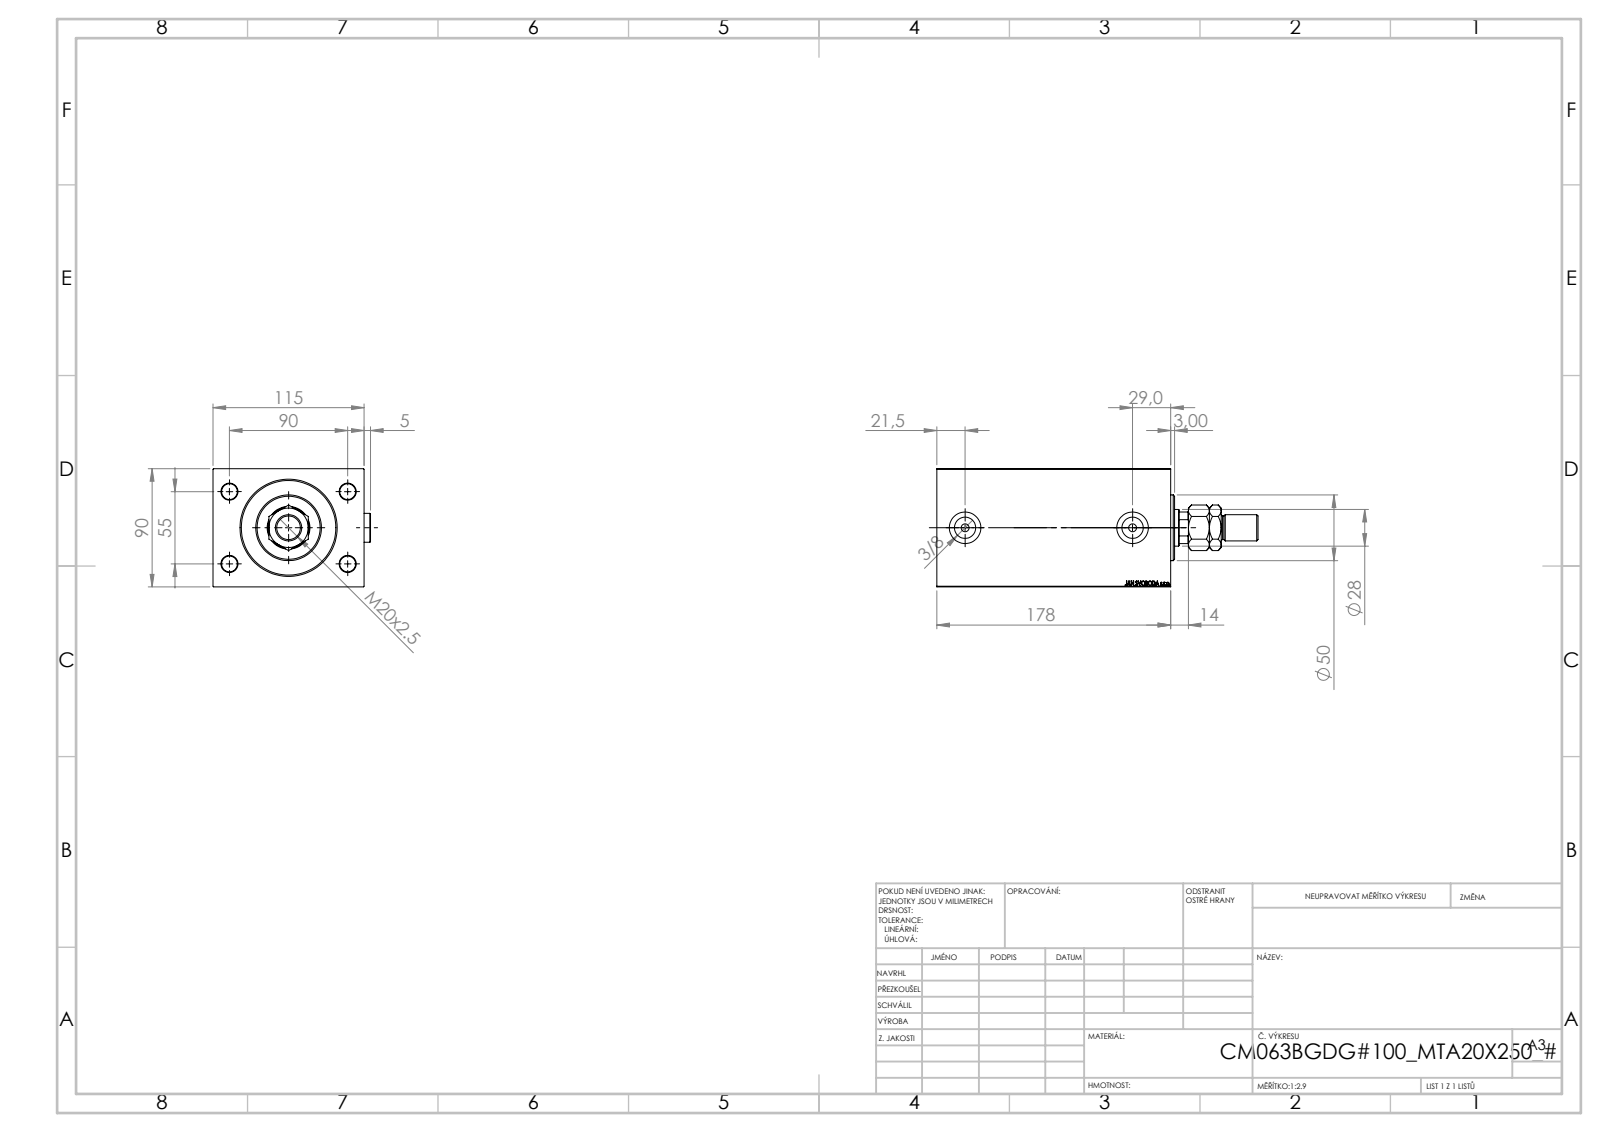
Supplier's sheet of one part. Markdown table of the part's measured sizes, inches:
| quantity | value |
| --- | --- |
| part name | V450CM_VC_B; MTA; V450CM_B_VCP; Zatka_OIL_PORT (+1 more) |
| STEP written by | SolidWorks 2019 (CONFIG_CONTROL_DESIGN) |
| units | inches |
| bodies | 6 solids, 987 faces (451 planar, 76 cylindrical, 460 other) |
| overall size | 9.626 × 4.72 × 3.543 |
| volume | 97.39 in³ |
| surface area | 283.5 in² |
| round holes (diameter × count) | 0.472 × 4, 0.236 × 2, 0.637 × 2, 0.945 × 2, 0.728 × 1, 1.102 × 1, 1.24 × 1, 1.28 × 1, 2.48 × 1, 2.559 × 1, 2.835 × 1 |
| round bosses / shafts (diameter × count) | 0.866 × 2, 1.969 × 1, 0.787 × 1, 0.709 × 1 |
| partial cylindrical surfaces (radius × count) | 0.531 × 1 |
| main face-to-face distances | 3.543, 4.528, 7.008, 6.319, 0.689, 0.531, 5.787, 6.476, 4.469, 3.937 |
| hole center spacings | 2.076, 2.165, 3.543, 4.153, 5.02 |
